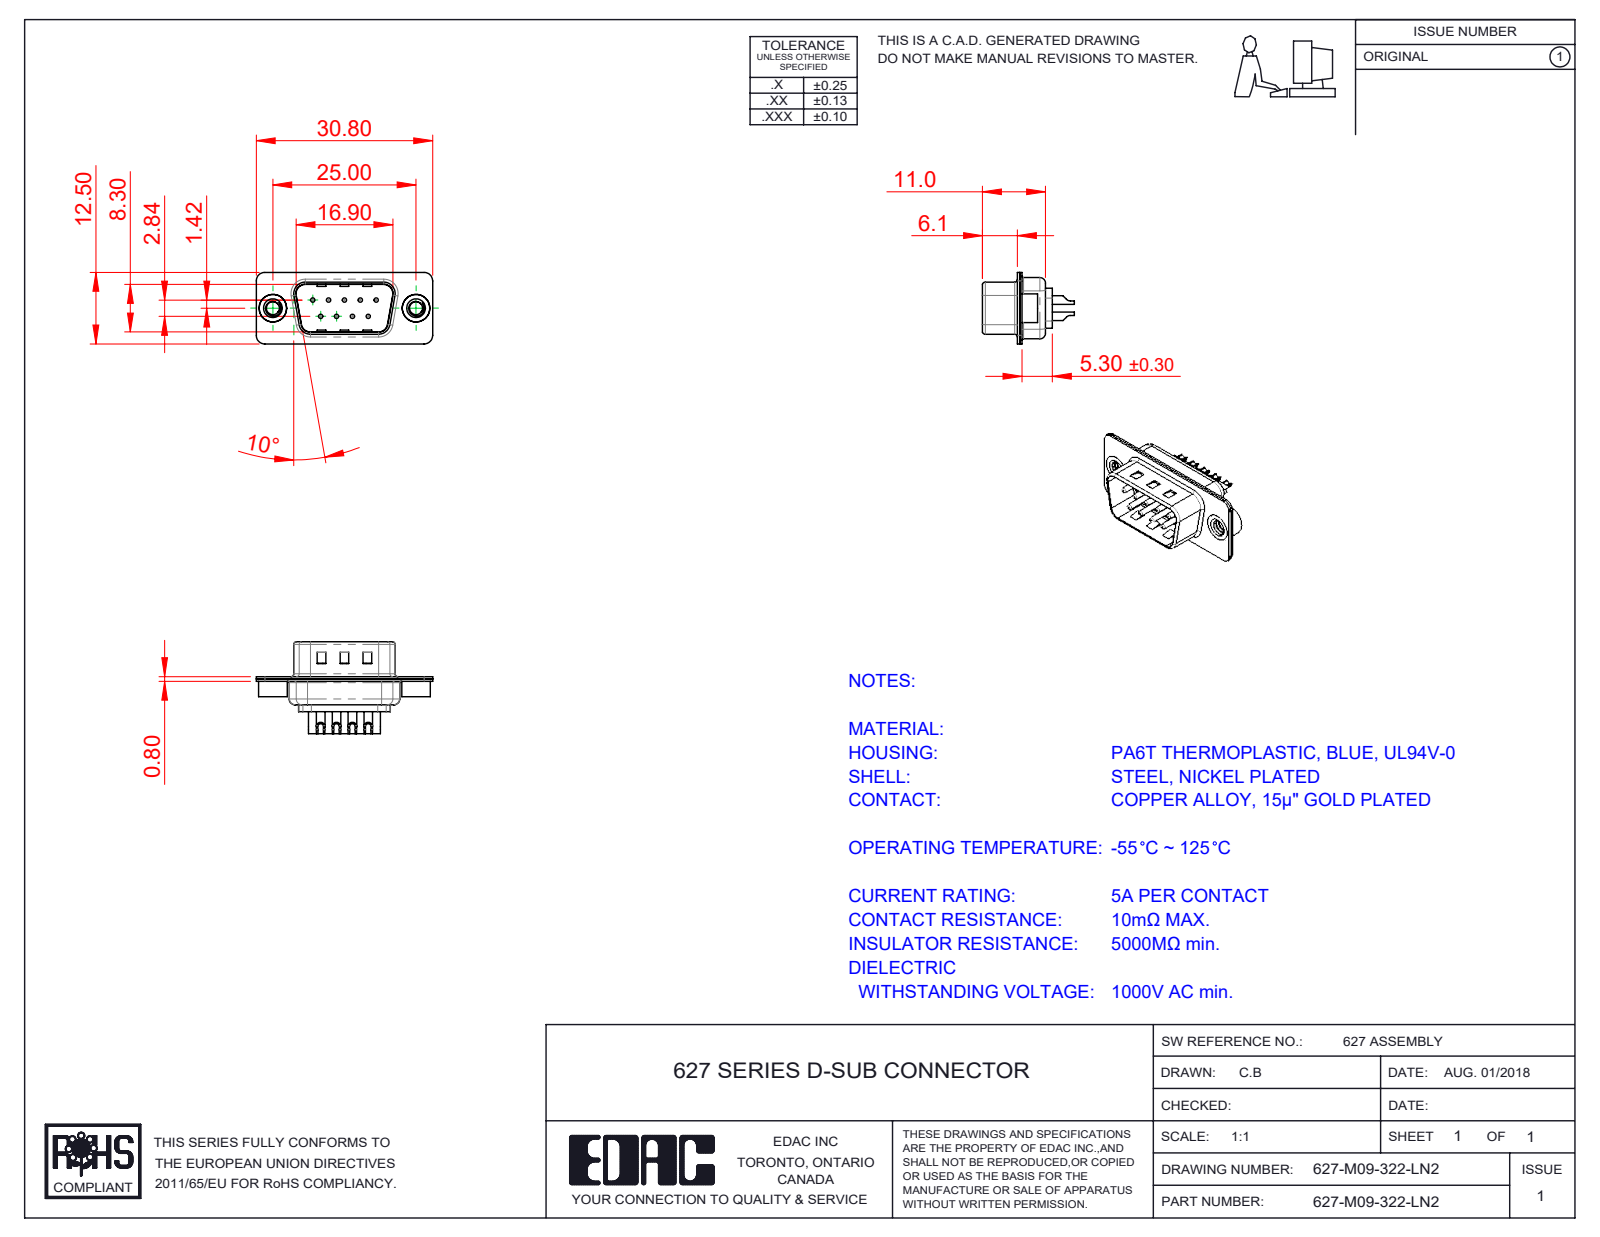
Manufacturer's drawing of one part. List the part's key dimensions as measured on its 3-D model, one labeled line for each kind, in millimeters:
Part name (STEP PRODUCT): 627M Contact Row 2_22; 627M Shell Front_09 Contacts; 627-M09-322-LN2; 627M Shell Rear_09 Contacts (+3 more)
STEP written by: SolidWorks 2020 (CONFIG_CONTROL_DESIGN)
Units: millimetres
Bodies: 14 solids, 637 faces (188 planar, 273 cylindrical, 176 other)
Overall size (bounding box): 30.8 × 16.05 × 12.5
Volume: 1 331 mm³ · Surface area: 3 658 mm²
Round holes (diameter × count): ⌀0.75 ×9, ⌀1 ×9, ⌀1.6 ×9, ⌀2 ×9, ⌀2.26 ×2, ⌀4 ×2, ⌀4.8 ×2
Round bosses / shafts (diameter × count): ⌀1.5 ×9, ⌀5 ×2, ⌀4.9 ×2
Partial cylindrical surfaces — rounded edges, fillets, slot ends (radius × count): R1.5 ×16, R2 ×12, R0.5 ×8, R1.6 ×8, R1 ×6, R0.25 ×4, R0.6 ×4, R0.65 ×4
Main face-to-face distances: 0.4, 0.8, 9.5, 9.1, 8.7, 0.65, 9.9, 1.2, 0.75, 0.35
Hole centre spacings: 3.16, 2.77, 5.54, 5.03, 5.04, 8.31, 7.1, 7.48
